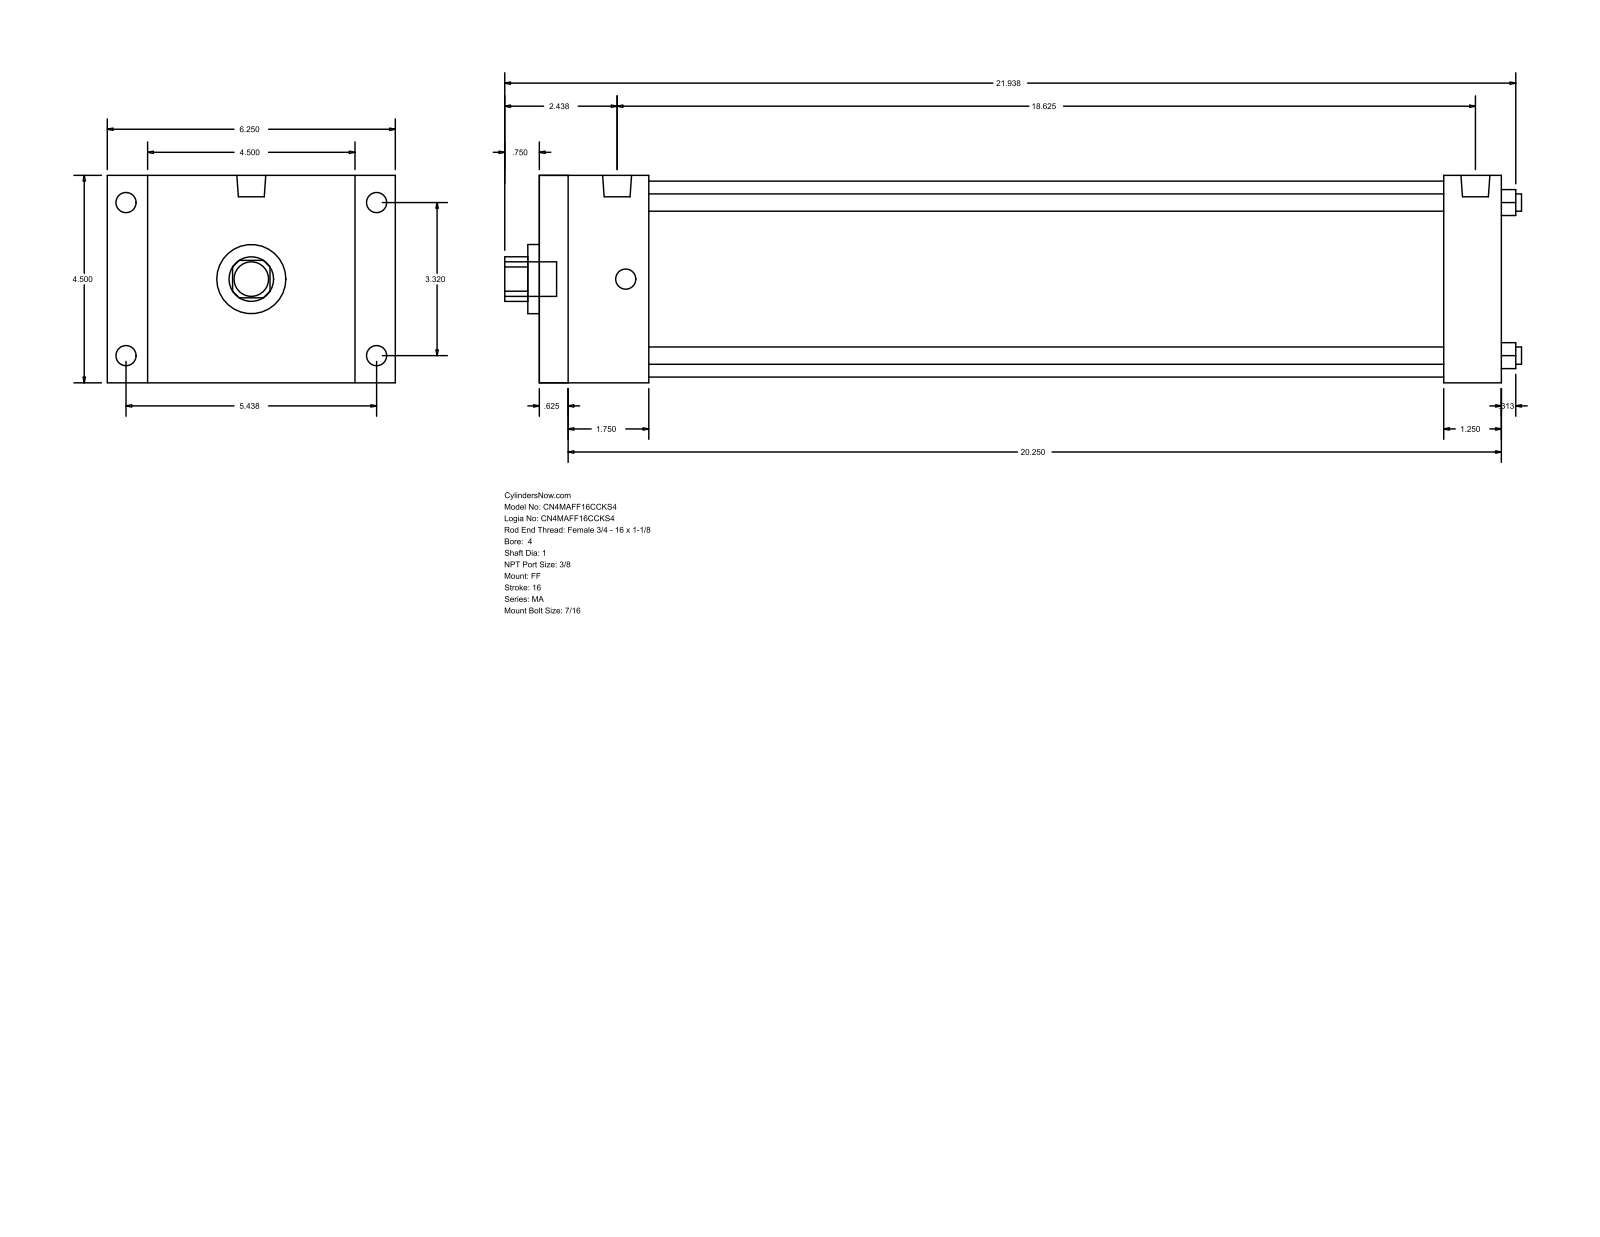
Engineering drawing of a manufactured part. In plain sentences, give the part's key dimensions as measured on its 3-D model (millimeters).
The part is named "MA_FF__0400_1". Its 3-D file was written by "GSSL Pune (CONFIG_CONTROL_DESIGN)". It is 0 solids with 92 faces: 64 planar, 28 cylindrical and 0 other. Overall it measures 560.39 by 158.75 by 114.3 millimeters. Round holes: 4 of diameter 9.53, 1 of diameter 25.4, 1 of diameter 38.1, 1 of diameter 107.95. Round bosses or shafts: 8 of diameter 11.11, 2 of diameter 15.93, 1 of diameter 19.05. Partial cylindrical surfaces (rounded edges, fillets, slot ends): 1 of radius 12.29. The main face-to-face distances are 114.3, 530.22, 15.87, 514.35, 22.23, 136.53, 498.47, 482.6, 31.75, 60.33. The hole center spacings are 59.62, 84.32, 119.25.
